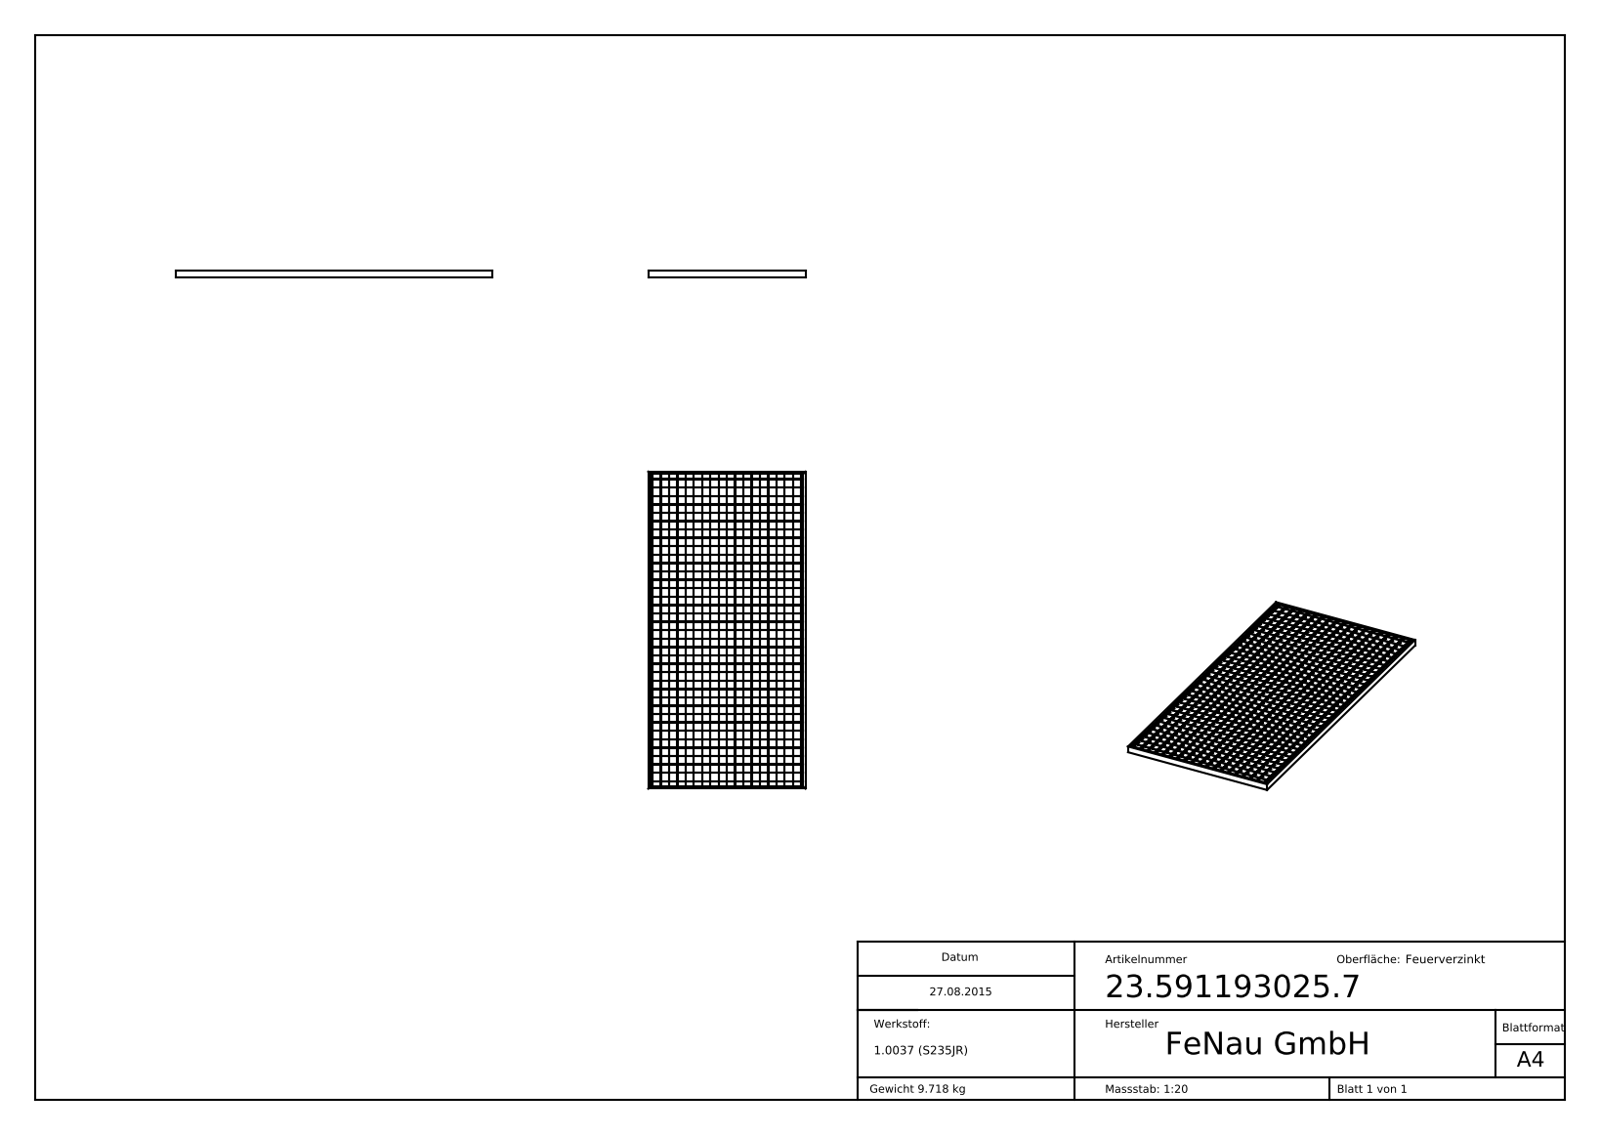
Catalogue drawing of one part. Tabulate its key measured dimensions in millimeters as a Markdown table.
| quantity | value |
| --- | --- |
| part name | 23-591193025-7 |
| STEP written by | SolidWorks 2015 (CONFIG_CONTROL_DESIGN) |
| units | millimeters |
| bodies | 1 solid, 2558 faces (2558 planar, 0 cylindrical, 0 other) |
| overall size | 1190 × 590 × 25 |
| volume | 1 246 000 mm³ |
| surface area | 1 834 000 mm² |
| main face-to-face distances | 63, 31.5, 94.5, 126, 157.5, 189, 220.5, 31, 252, 283.5 |
